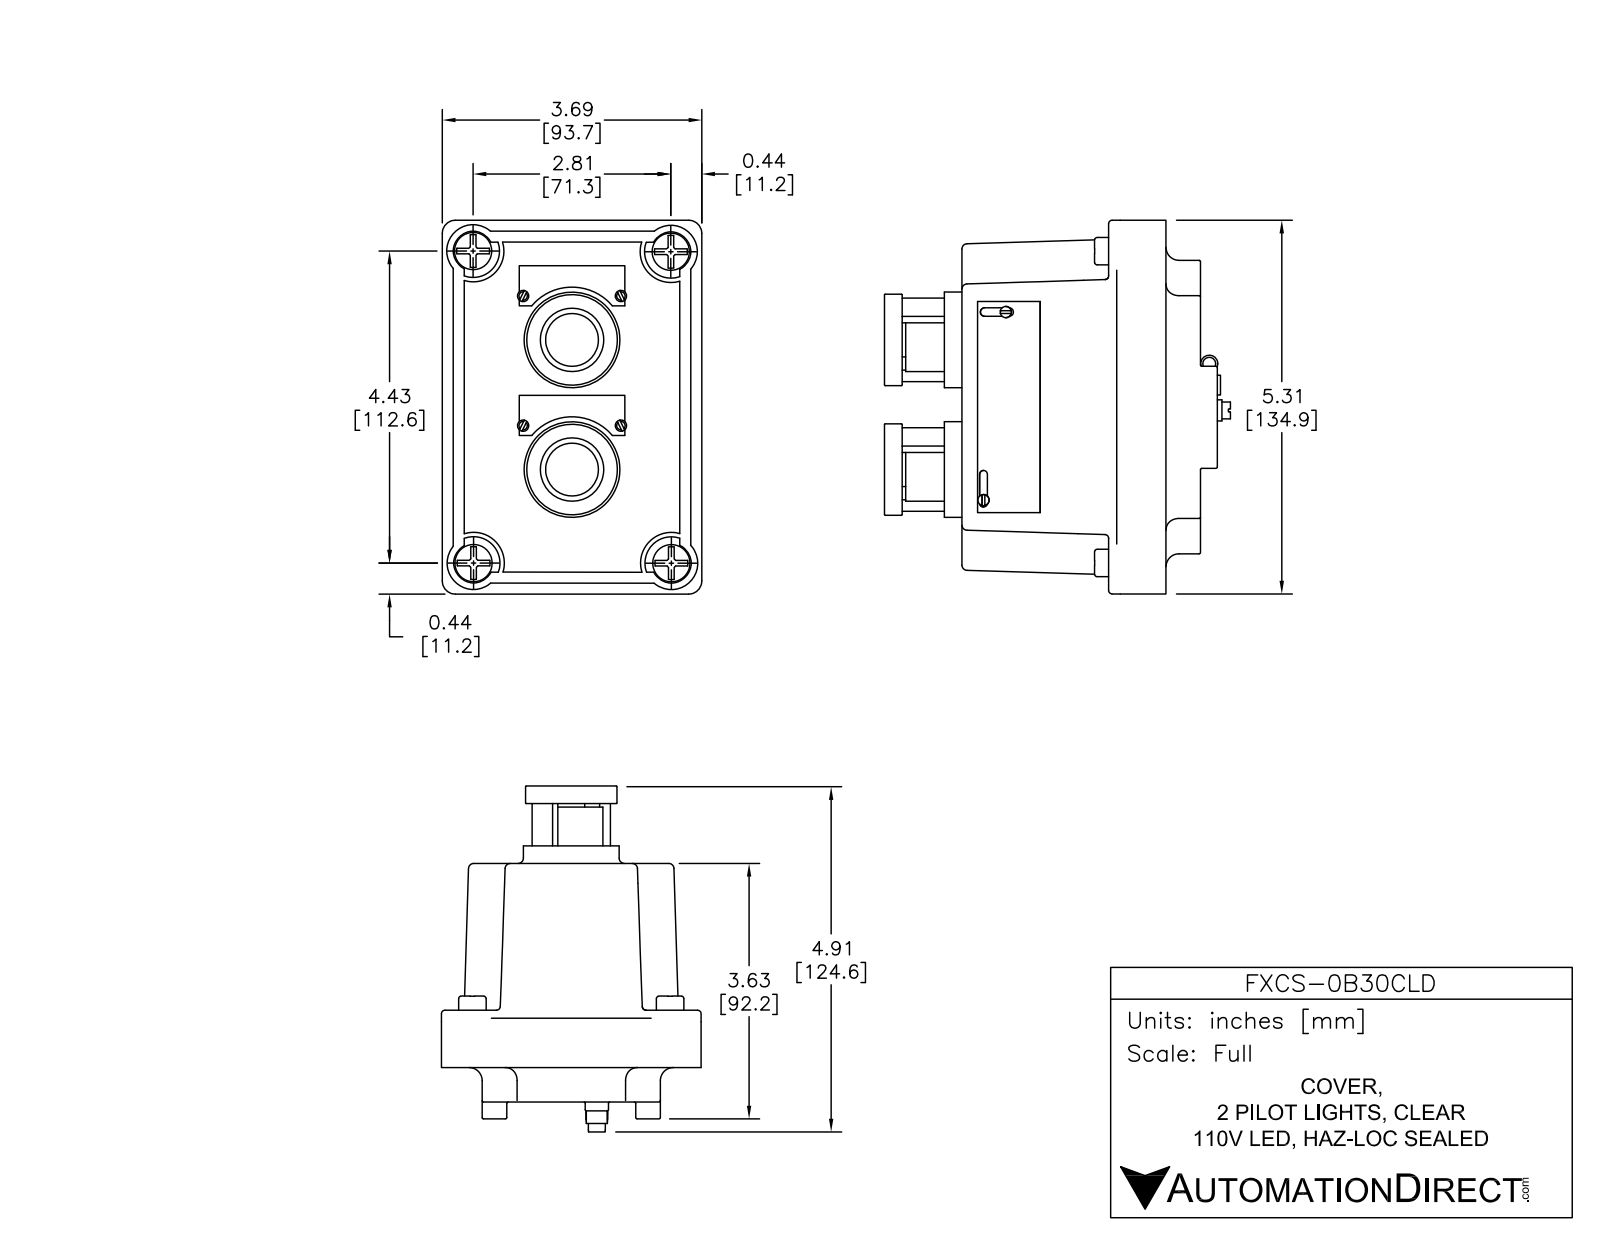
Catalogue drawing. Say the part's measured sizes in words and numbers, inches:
The part is named "FXCS-0B30CLD". Its 3-D file was written by "SolidWorks 2015 (AUTOMOTIVE_DESIGN)". It is 1 solid with 746 faces: 314 planar, 165 cylindrical and 267 other. Overall it measures 5.31 by 4.989 by 3.69 inches. Its volume is 49.86 cubic inches and its surface area 106.4 square inches. Round holes: 8 of diameter 0.16, 1 of diameter 0.198, 1 of diameter 0.9, 1 of diameter 0.94. Round bosses or shafts: 8 of diameter 0.16, 4 of diameter 0.39, 2 of diameter 1.36, 2 of diameter 1.3, 1 of diameter 0.9, 1 of diameter 0.33, 1 of diameter 0.3, 1 of diameter 0.24. Partial cylindrical surfaces (rounded edges, fillets, slot ends): 22 of radius 0.02, 12 of radius 0.05, 4 of radius 0.055, 4 of radius 0.06, 4 of radius 0.075, 4 of radius 0.185, 4 of radius 0.42, 3 of radius 0.653. The main face-to-face distances are 0.49, 3.39, 2.9, 0.02, 3.69, 0.578, 3.111, 0.25, 1.19, 0.7. The hole center spacings are 0.25, 2.197, 0.5, 2.183, 2.239, 0.75, 1.168, 1.279.
